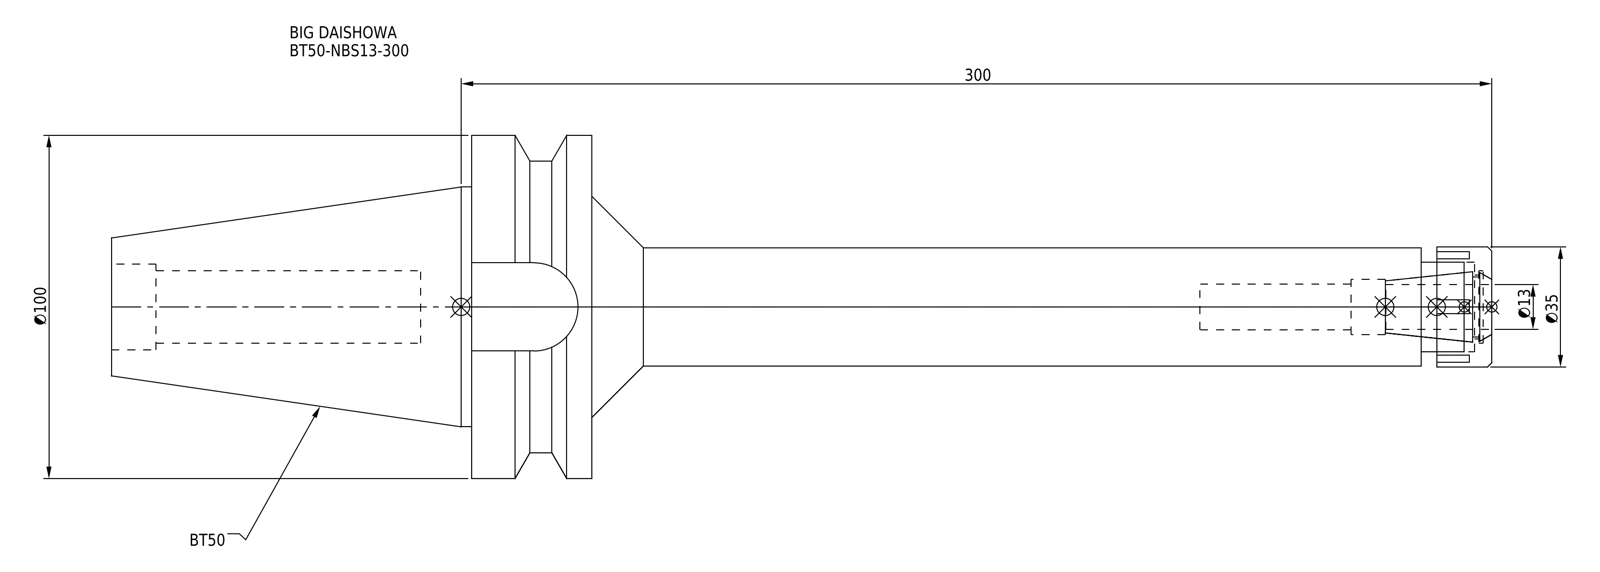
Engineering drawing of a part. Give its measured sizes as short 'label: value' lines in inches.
name: NBN13_1.stp; DXF_TEMP_ASSY_ASM_4_ASM.stp; BT50-NBS13-300.stp; BT50-NBS13-300 (+3 more)
written by: SolidWorks 2019 (CONFIG_CONTROL_DESIGN)
unit: in
bodies: 2 solids, 89 faces (45 planar, 30 cylindrical, 14 other)
size: 15.819 × 3.937 × 3.937
volume: 42.86 in³; area: 133.5 in²
holes: 1× ⌀0.524, 1× ⌀0.63, 1× ⌀0.728, 1× ⌀0.827, 1× ⌀0.835, 1× ⌀0.984, 1× ⌀1.024
bosses: 1× ⌀3.937, 1× ⌀3.346, 1× ⌀2.75, 1× ⌀1.378, 1× ⌀1.358
rounds: 1× R0.506
face distances: 1.378, 5.504, 4.126, 2.787, 10.315, 11.693, 15.819, 0.807, 0.315, 1.012
